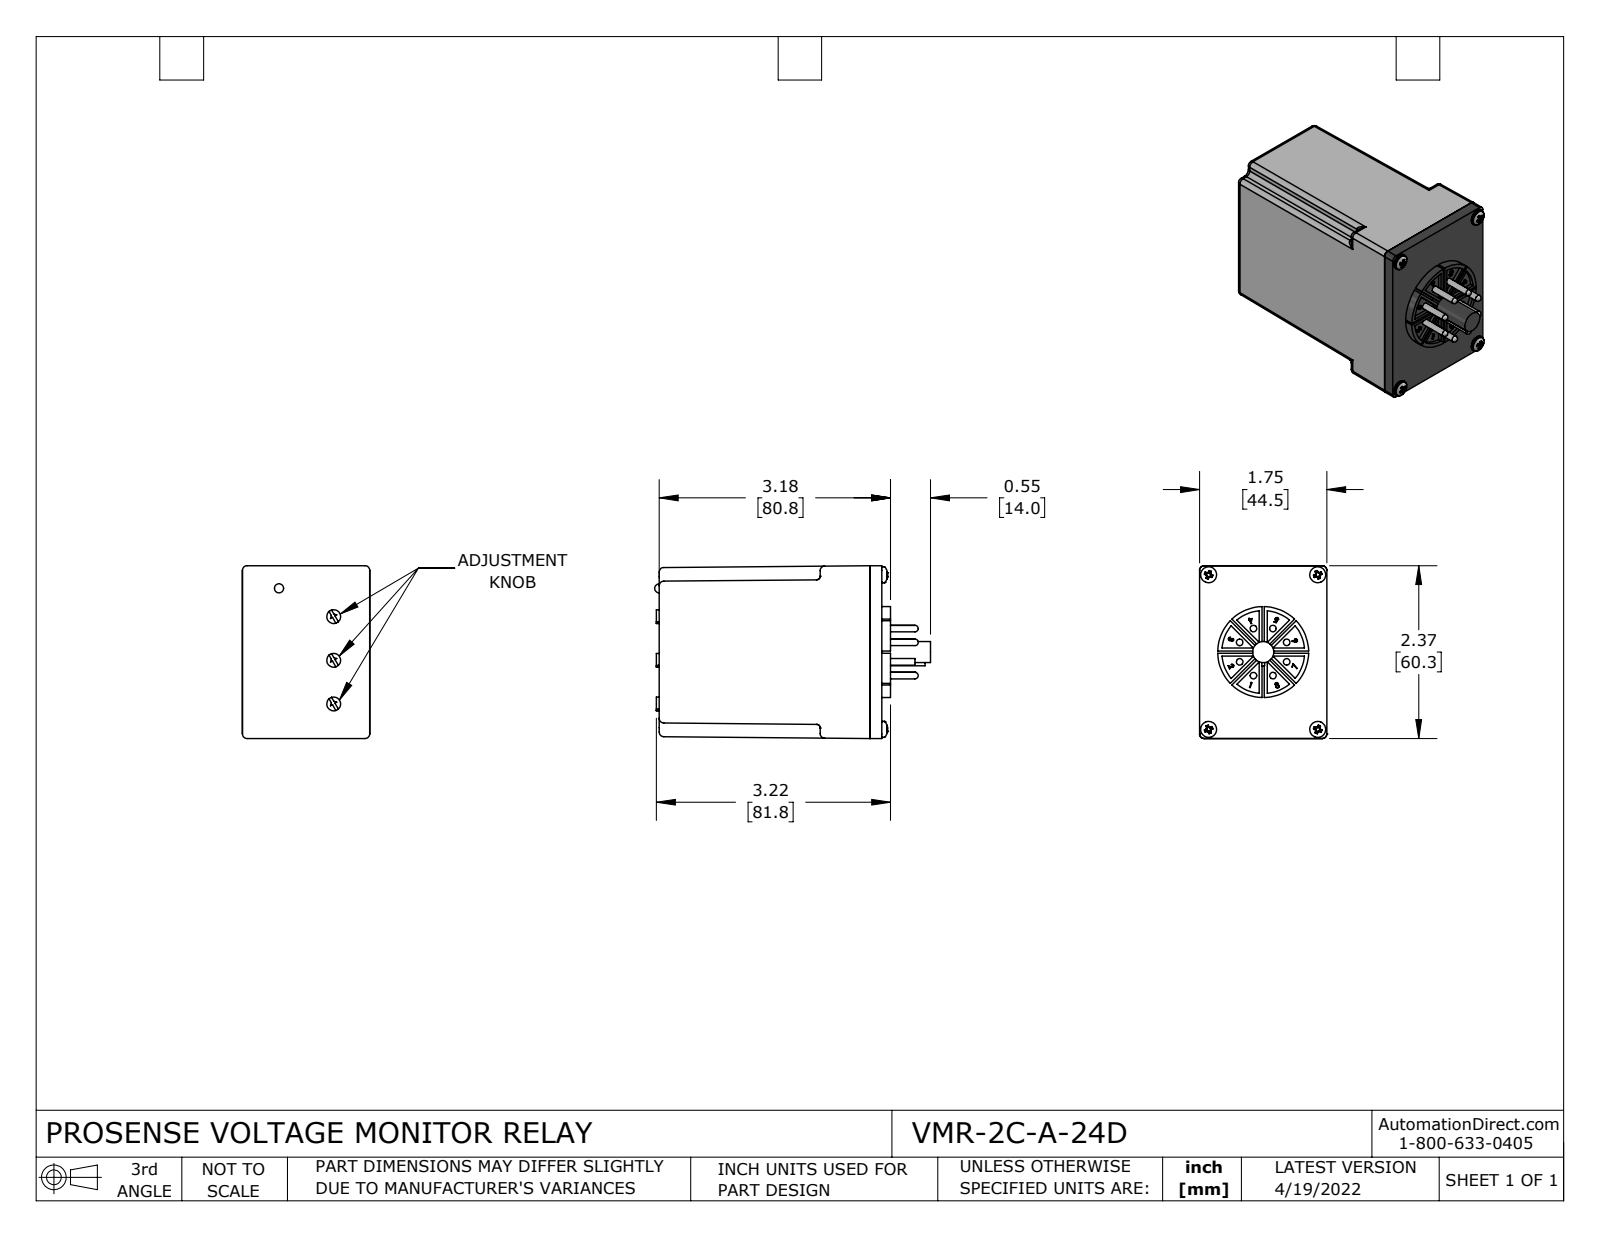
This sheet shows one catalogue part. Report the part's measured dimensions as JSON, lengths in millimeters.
{"part_name": "VMR-2C-A-24D", "step_written_by": "SolidWorks 2021 (CONFIG_CONTROL_DESIGN)", "units": "millimeters", "bodies": {"solids": 18, "faces": 574, "planar": 249, "cylindrical": 170, "other": 155}, "overall_size": [96.3, 60.3, 44.5], "volume_mm3": 200700, "surface_area_mm2": 28850, "round_holes": [[3.2, 4]], "round_bosses_or_shafts": [[2.3, 8], [5.6, 4], [4.8, 3], [31.8, 1], [7.4, 1]], "partial_cylinders_radius": [[1.6, 32], [0.1, 8], [1.3, 4], [14.5, 1]], "face_to_face_distances": [73.7, 4.1, 77.7, 1.8, 5.8, 79.5, 4.8, 1.3, 3, 7.1], "hole_center_spacings": [38.1, 54, 66.1]}
